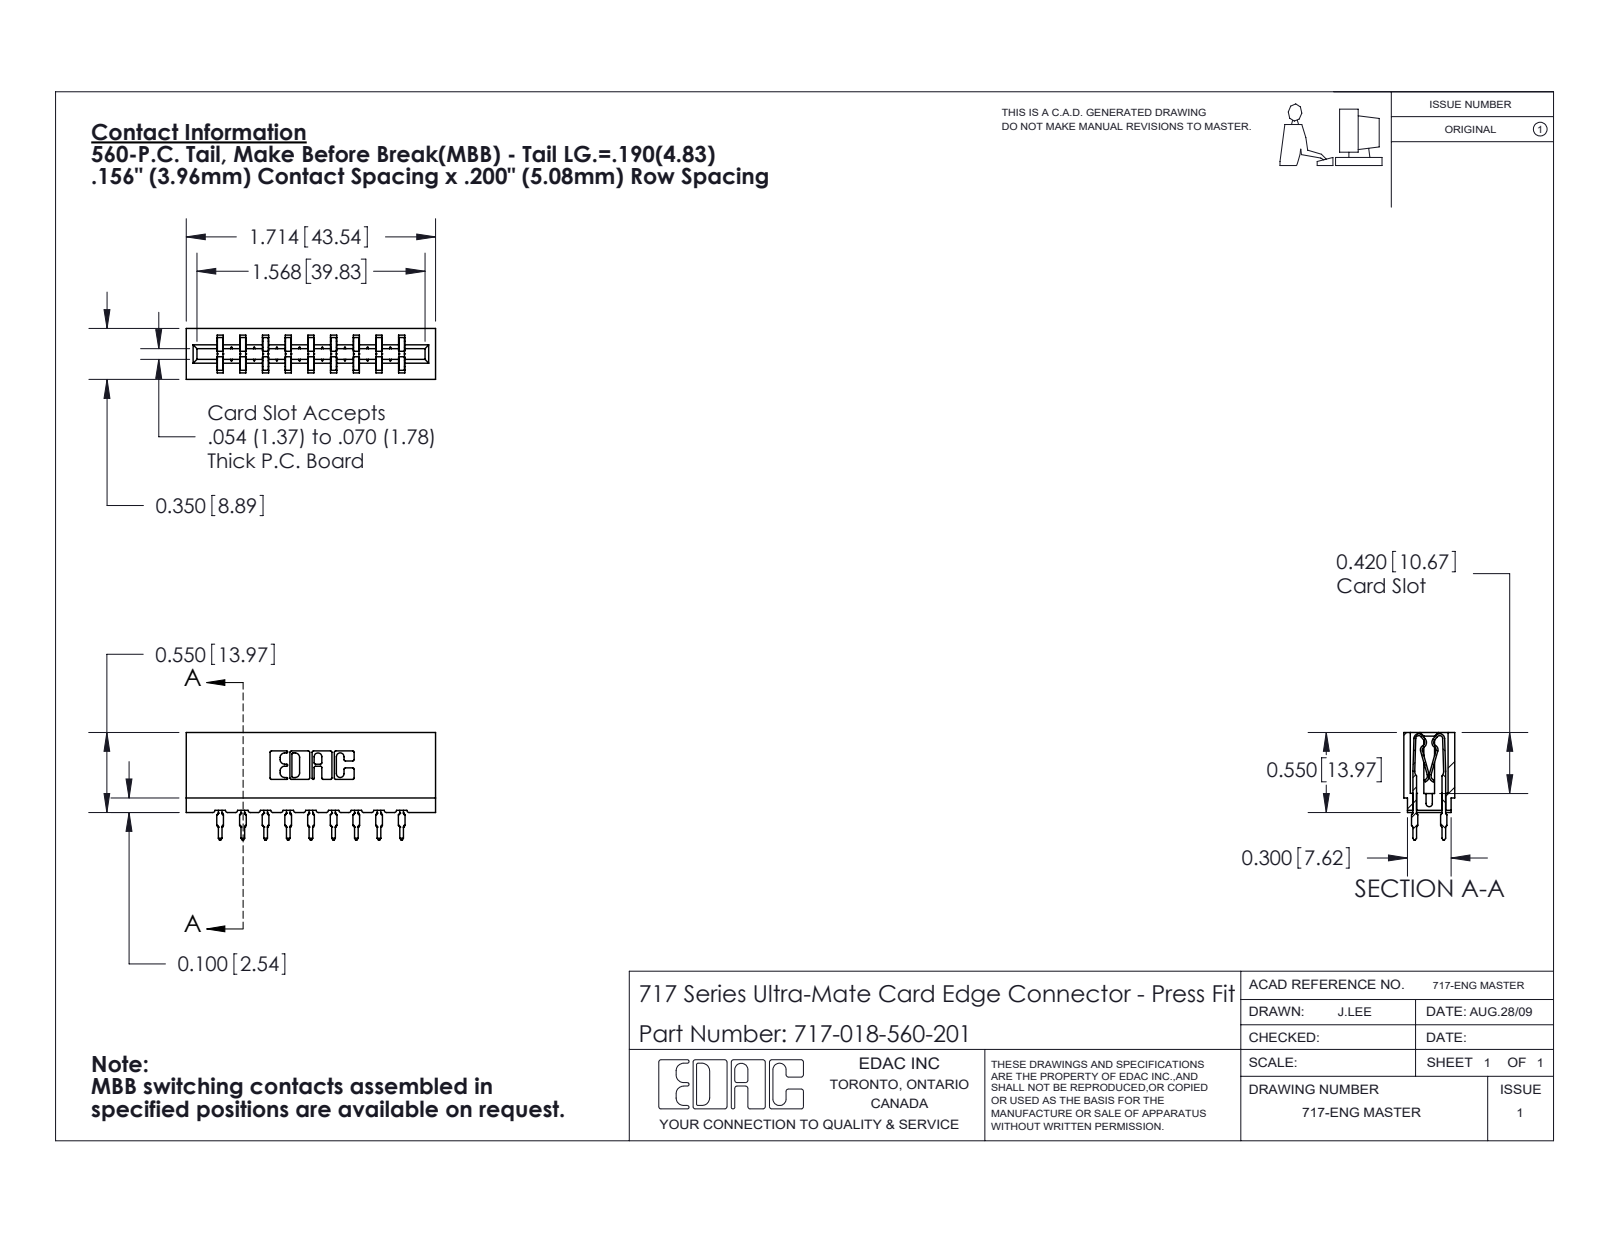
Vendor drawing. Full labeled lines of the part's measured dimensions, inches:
Part name (STEP PRODUCT): 745-292-001_560; 717-018-560-201; 717 Part_Insulator Option - 06
STEP written by: SolidWorks 2020 (CONFIG_CONTROL_DESIGN)
Units: inches
Bodies: 19 solids, 1876 faces (981 planar, 427 cylindrical, 468 other)
Overall size (bounding box): 1.714 × 0.739 × 0.35
Volume: 0.243 in³ · Surface area: 9.23 in²
Partial cylindrical surfaces — rounded edges, fillets, slot ends (radius × count): R0.021 ×36, R0.01 ×22, R0.015 ×18, R0.005 ×8, R0.011 ×8, R0.007 ×6, R0.031 ×6, R0.026 ×3
Main face-to-face distances: 0.156, 0.212, 0.624, 0.138, 0.468, 0.198, 0.35, 0.312, 0.042, 0.312
